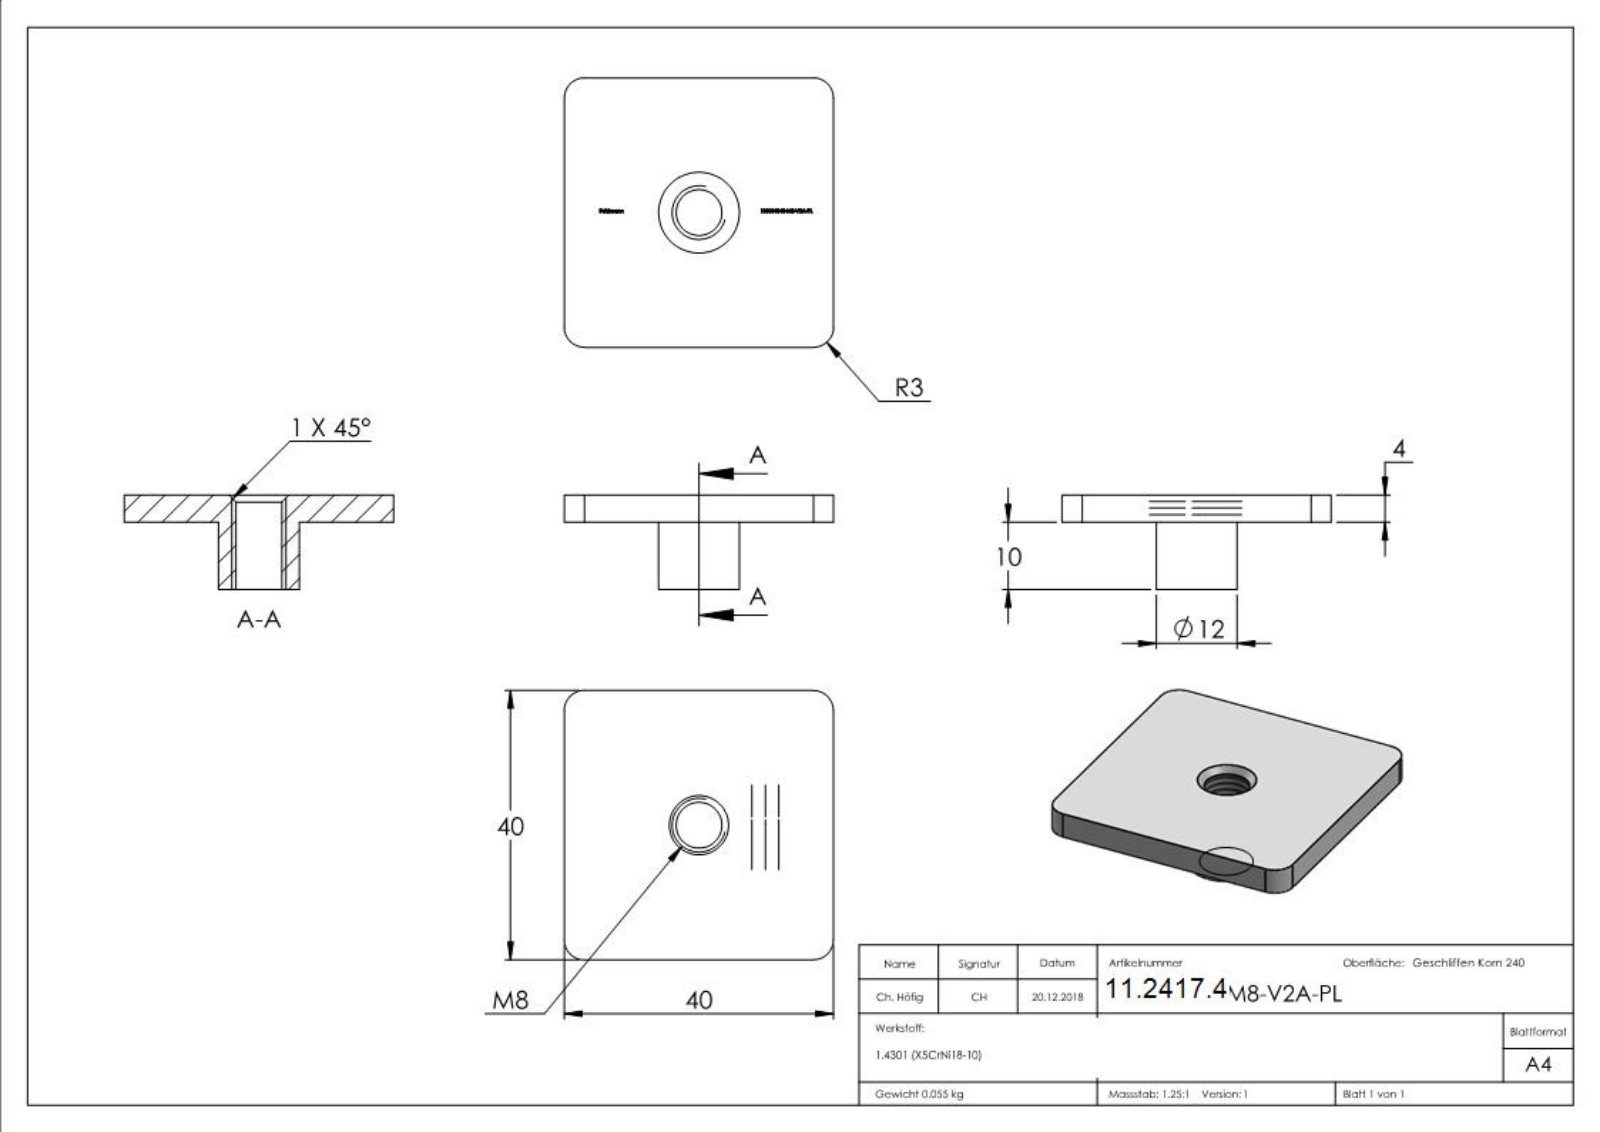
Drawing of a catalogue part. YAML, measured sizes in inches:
part_name: "100034040-M8-V2A-PL"
step_written_by: "SolidWorks 2015 (CONFIG_CONTROL_DESIGN)"
units: inches
bodies: {solids: 1, faces: 346, planar: 200, cylindrical: 8, other: 138}
overall_size: [1.575, 1.575, 0.551]
volume: 0.426
surface_area: 6.823
round_holes:
  - {diameter: 0.268, count: 1}
round_bosses_or_shafts:
  - {diameter: 0.472, count: 1}
partial_cylinders:
  - {radius: 0.118, count: 4}
face_to_face_distances: [0.157, 1.575, 0.394, 0.551, 0.398, 0.154, 0.787, 0.794, 0.78, 0.014]
